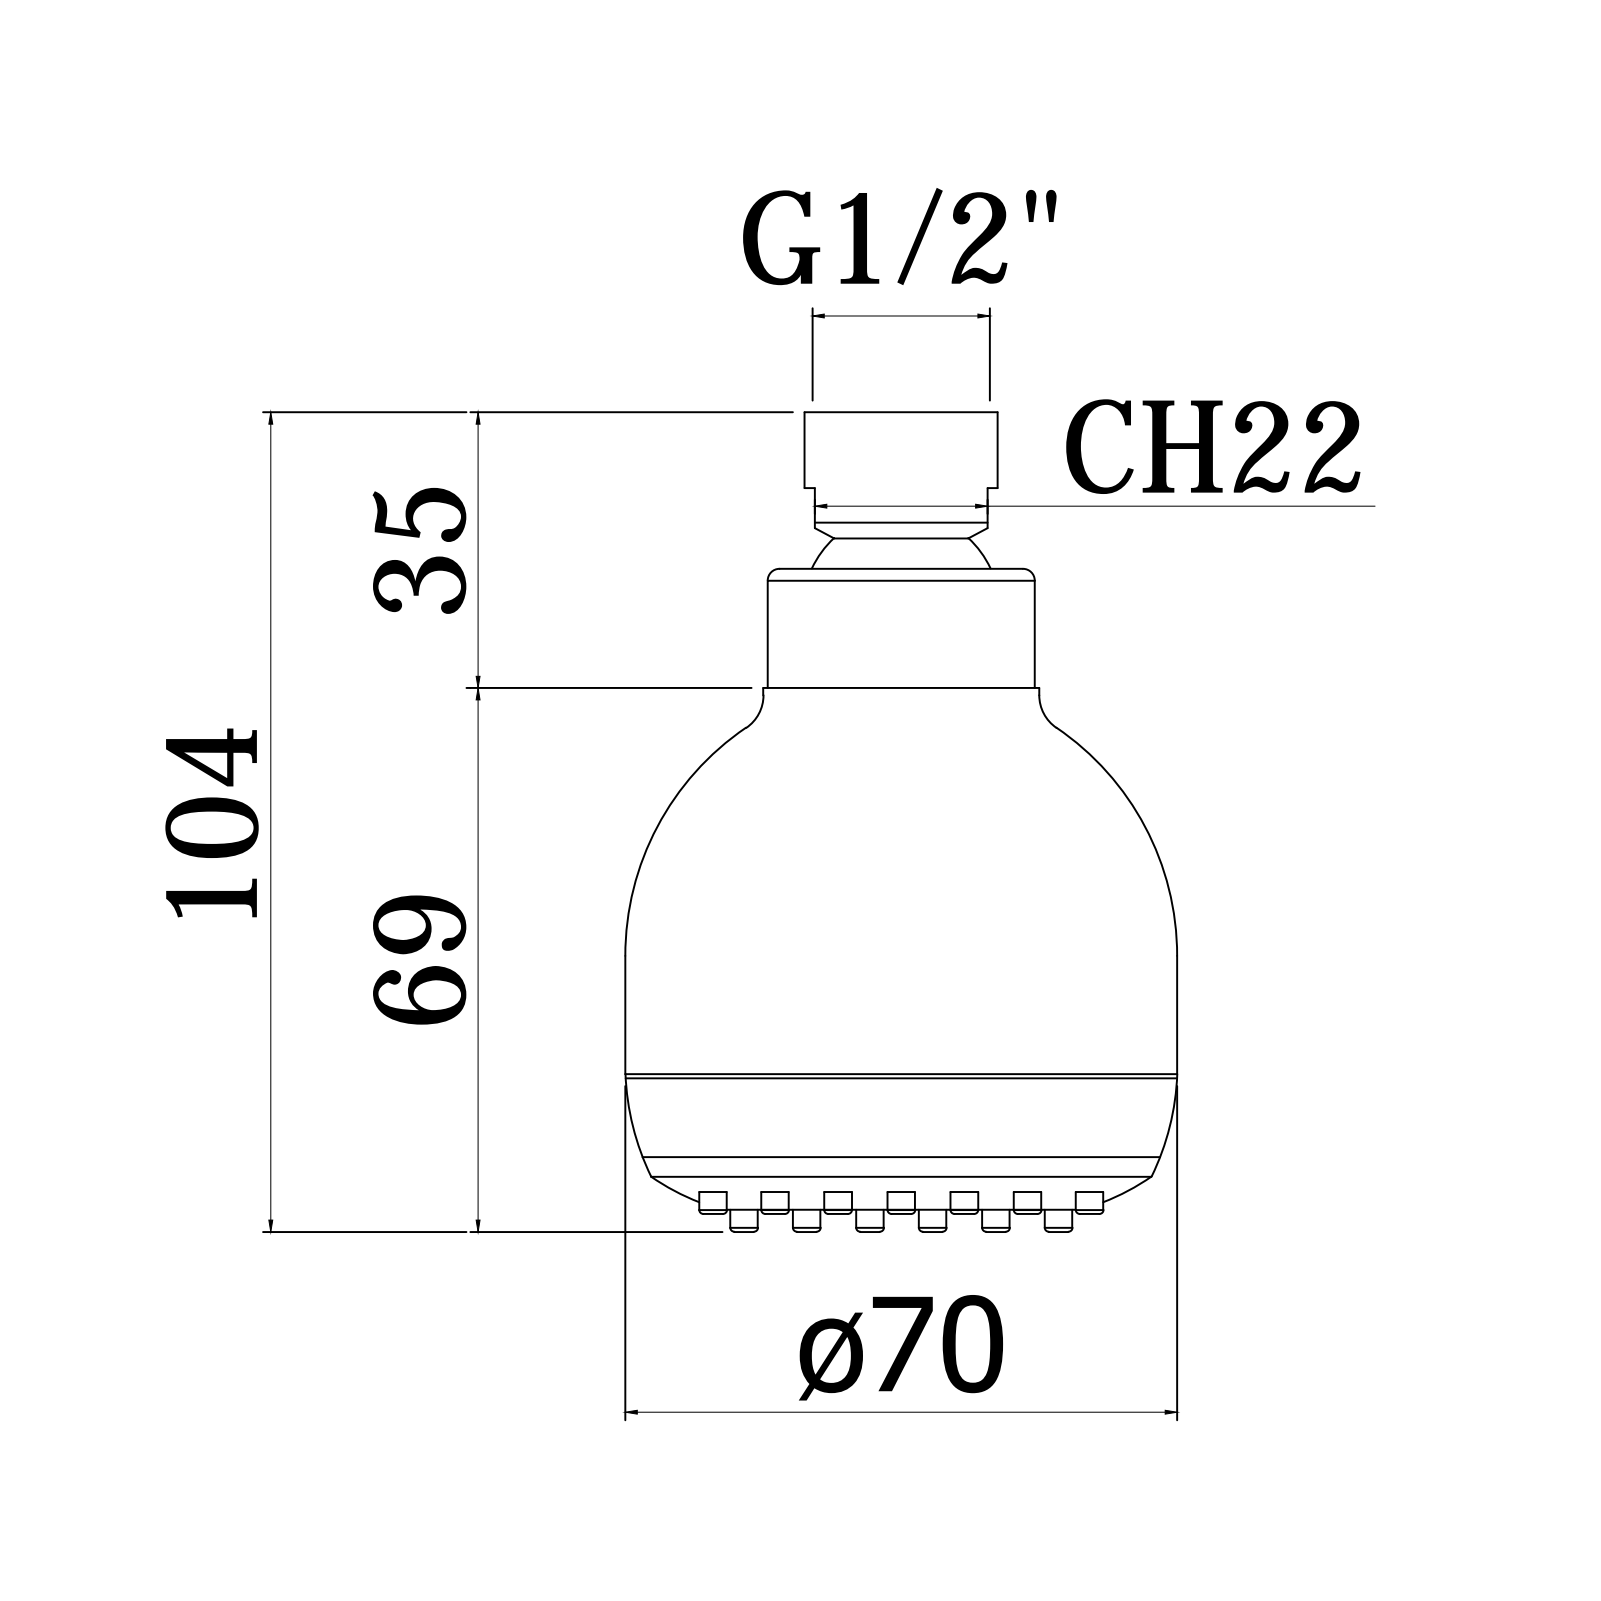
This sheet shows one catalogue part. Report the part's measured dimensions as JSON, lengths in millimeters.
{"part_name": "ZSOF031CR", "step_written_by": "CREO PARAMETRIC BY PTC INC, 2020044 (CONFIG_CONTROL_DESIGN)", "units": "millimeters", "bodies": {"solids": 0, "faces": 4182, "planar": 2439, "cylindrical": 1199, "other": 544}, "overall_size": [103.66, 70.86, 70.86], "round_holes": [[4.55, 20], [5.01, 19], [1.6, 9], [5, 5], [4, 3], [3.4, 1], [6.8, 1], [10, 1], [12.7, 1], [13, 1], [13.95, 1], [19.8, 1]], "round_bosses_or_shafts": [[5, 3], [3, 2], [70, 1], [61.3, 1], [58.6, 1], [46, 1], [40.7, 1], [35.5, 1]], "partial_cylinders_radius": [[0.5, 22], [1.4, 18], [2, 9], [10, 6], [1, 4], [0.4, 3], [4.5, 3], [25, 3]], "face_to_face_distances": [1.8, 2.4, 4.2, 1.6, 1.5, 1.65, 1.3, 4.5, 12.6, 14.4], "hole_center_spacings": [21.22, 6.64, 10, 18.79, 19.27, 3.47, 13.12, 17.32]}
